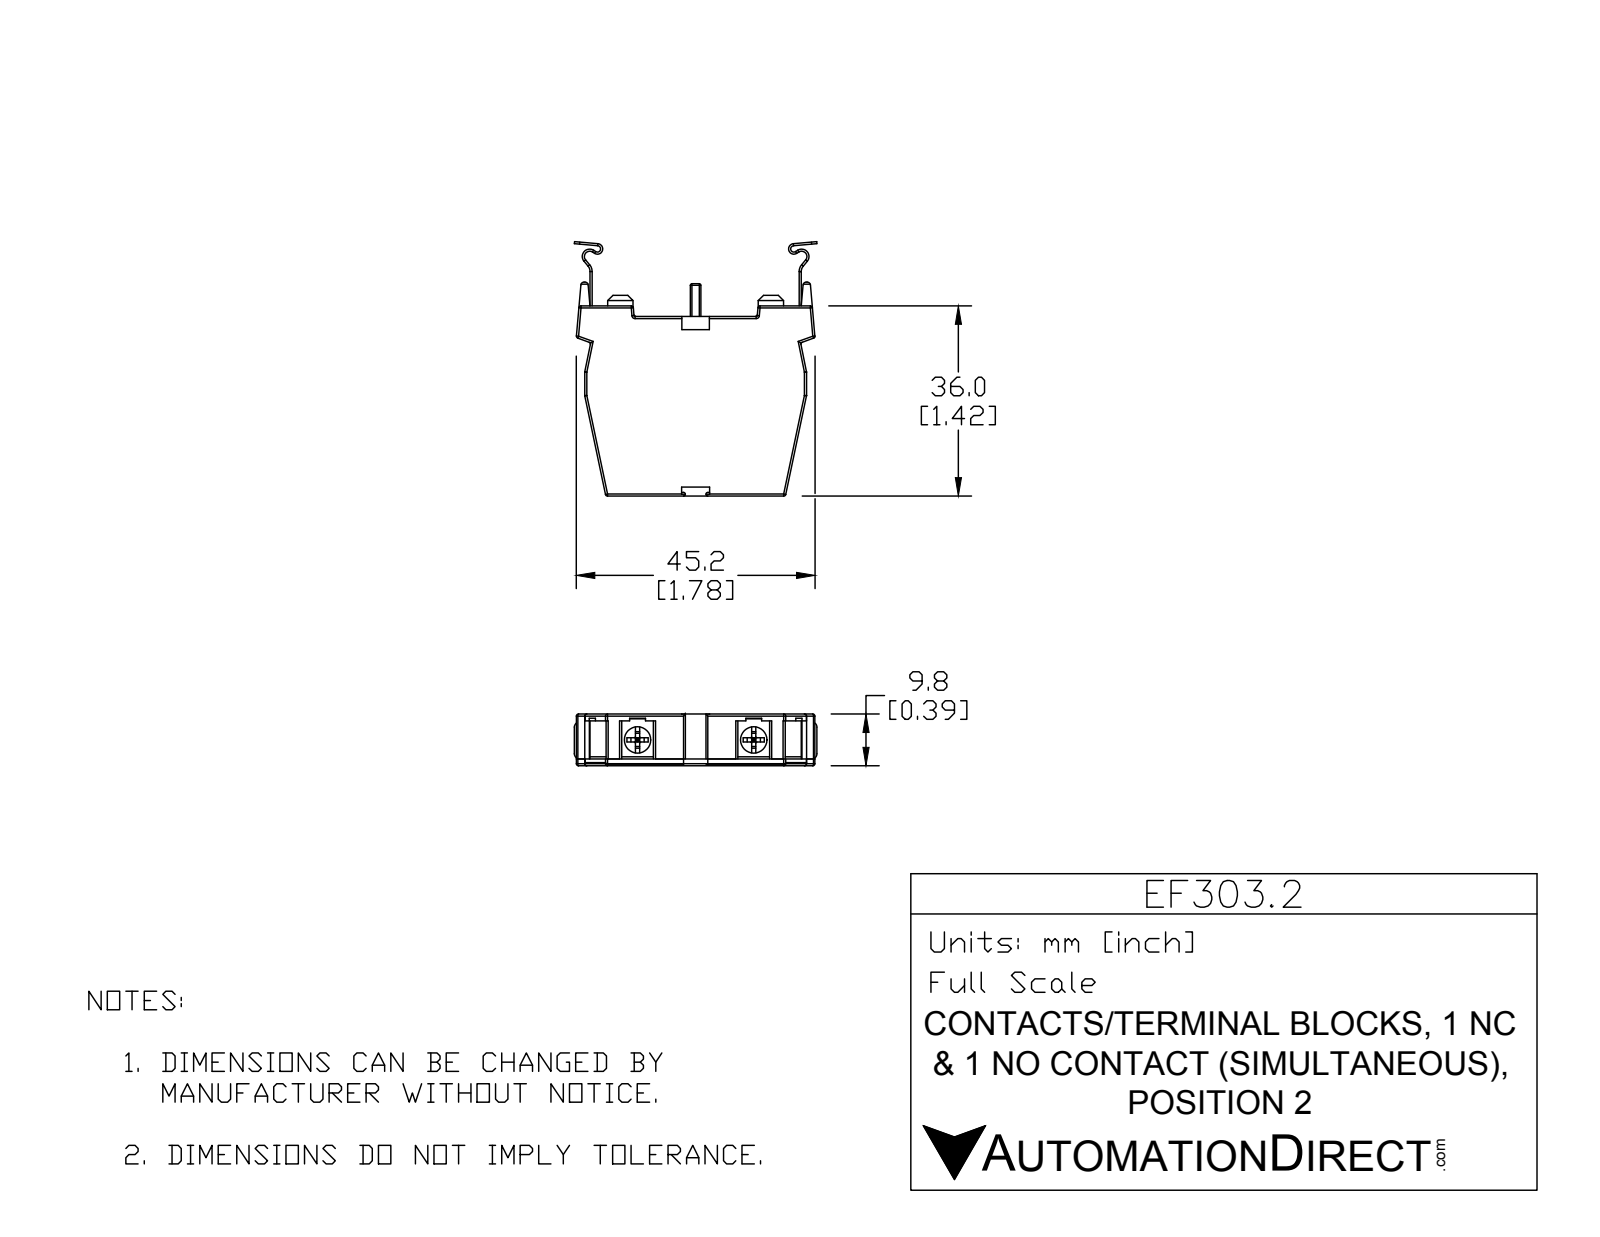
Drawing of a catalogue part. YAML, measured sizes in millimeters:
part_name: "EF303.2"
step_written_by: "SolidWorks 2015 (AUTOMOTIVE_DESIGN)"
units: millimeters
bodies: {solids: 7, faces: 299, planar: 173, cylindrical: 104, other: 22}
overall_size: [48.16, 46.28, 9.8]
volume: 12135
surface_area: 6604
round_holes:
  - {diameter: 5, count: 4}
round_bosses_or_shafts:
  - {diameter: 4, count: 4}
  - {diameter: 4.75, count: 2}
partial_cylinders:
  - {radius: 0.25, count: 44}
  - {radius: 0.5, count: 8}
  - {radius: 1, count: 6}
  - {radius: 0.6, count: 4}
  - {radius: 0.6, count: 2}
  - {radius: 1, count: 2}
  - {radius: 1.4, count: 2}
  - {radius: 1.6, count: 2}
face_to_face_distances: [9.8, 1.4, 8.4, 34, 7, 2, 0.4, 3.18, 37.18, 36]
hole_center_spacings: [21.81]
